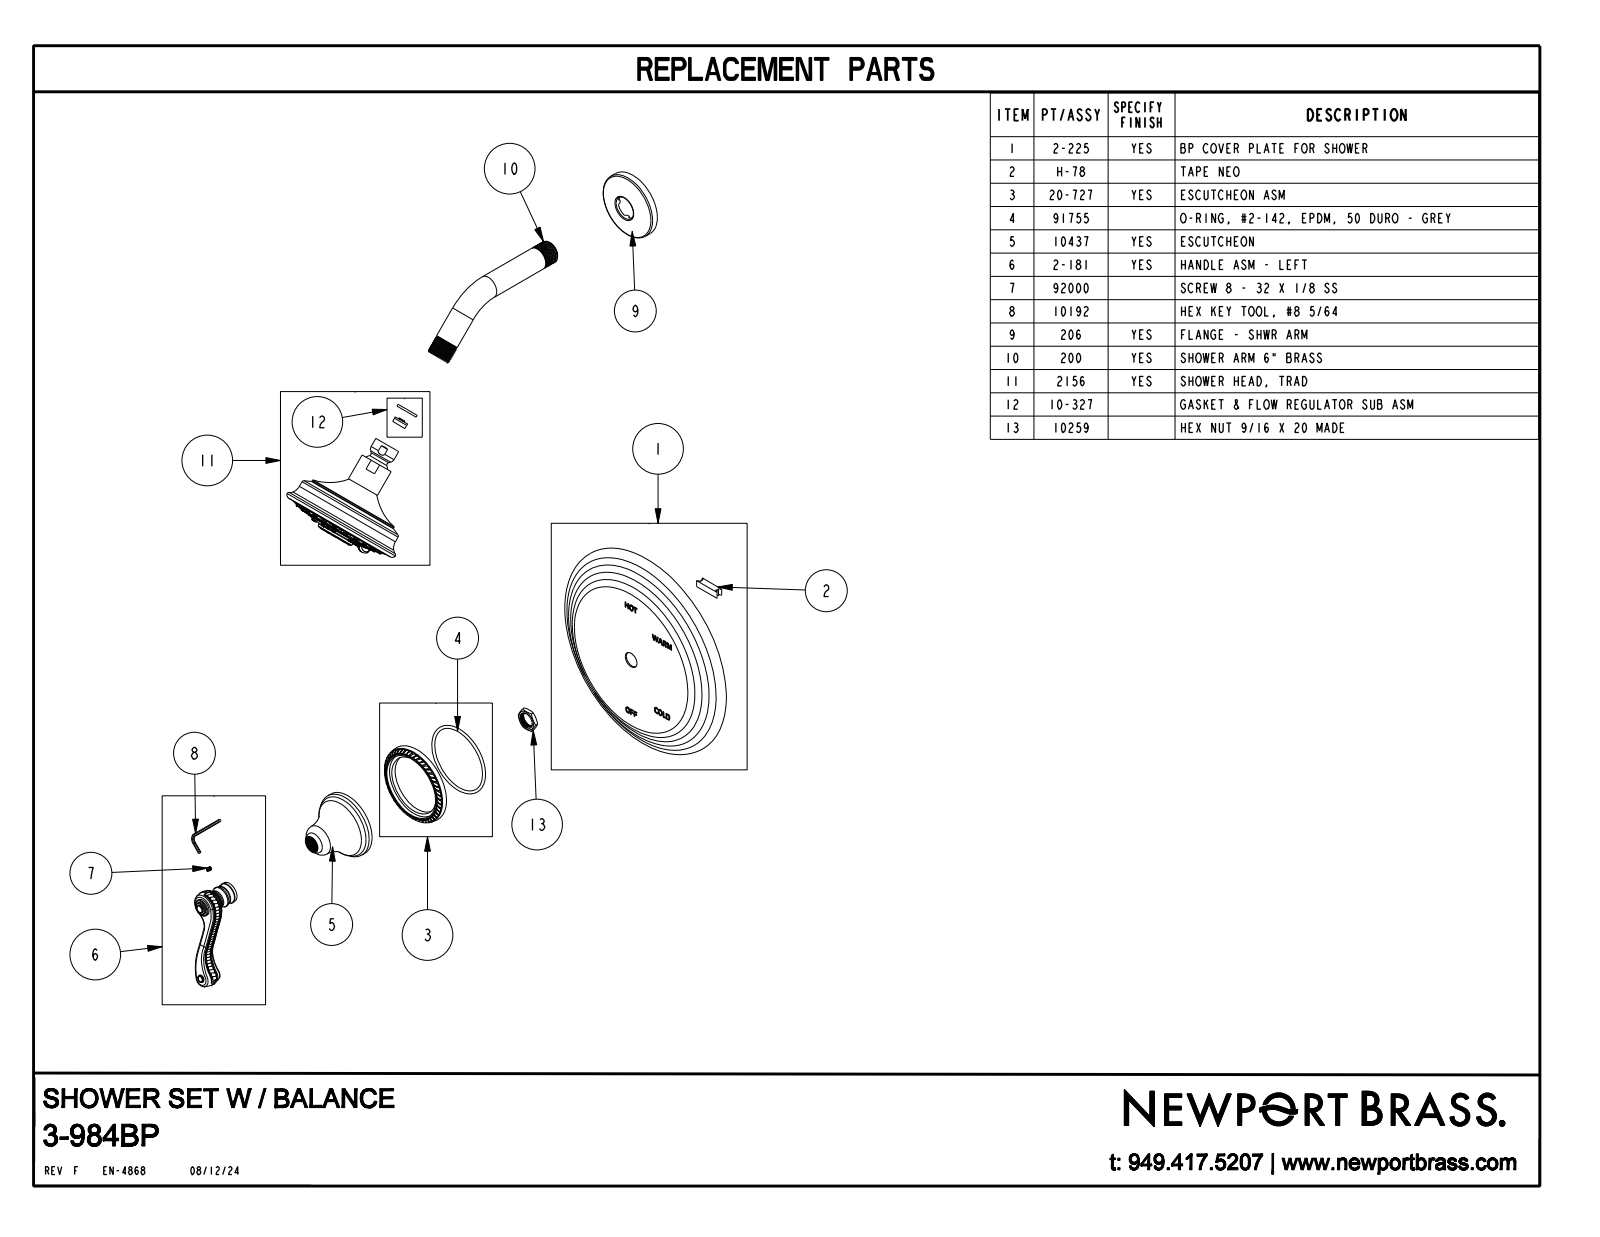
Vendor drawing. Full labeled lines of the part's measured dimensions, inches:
Part name (STEP PRODUCT): 3-984BP
STEP written by: CREO PARAMETRIC BY PTC INC, 2018400 (CONFIG_CONTROL_DESIGN)
Units: inches
Bodies: 2 solids, 1818 faces (365 planar, 312 cylindrical, 1141 other)
Overall size (bounding box): 17.065 × 8.25 × 7.75
Volume: 53.47 in³ · Surface area: 193.4 in²
Round holes (diameter × count): ⌀0.059 ×8, ⌀0.925 ×1
Round bosses / shafts (diameter × count): ⌀0.142 ×39, ⌀0.165 ×23, ⌀0.813 ×2, ⌀0.26 ×2, ⌀3.81 ×1, ⌀3.724 ×1, ⌀3.24 ×1, ⌀2.38 ×1
Partial cylindrical surfaces — rounded edges, fillets, slot ends (radius × count): R0.15 ×49, R0.09 ×25, R0.12 ×24, R0.079 ×8, R0.02 ×2, R11 ×2, R0.121 ×1, R0.137 ×1
Main face-to-face distances: 0.754, 0.063, 0.118, 0.181, 3.984, 3.23, 3.494, 2.74, 0.49, 1.044
Hole centre spacings: 0.443, 0.579, 0.818, 0.819, 1.069, 0.443, 0.578, 1.069
